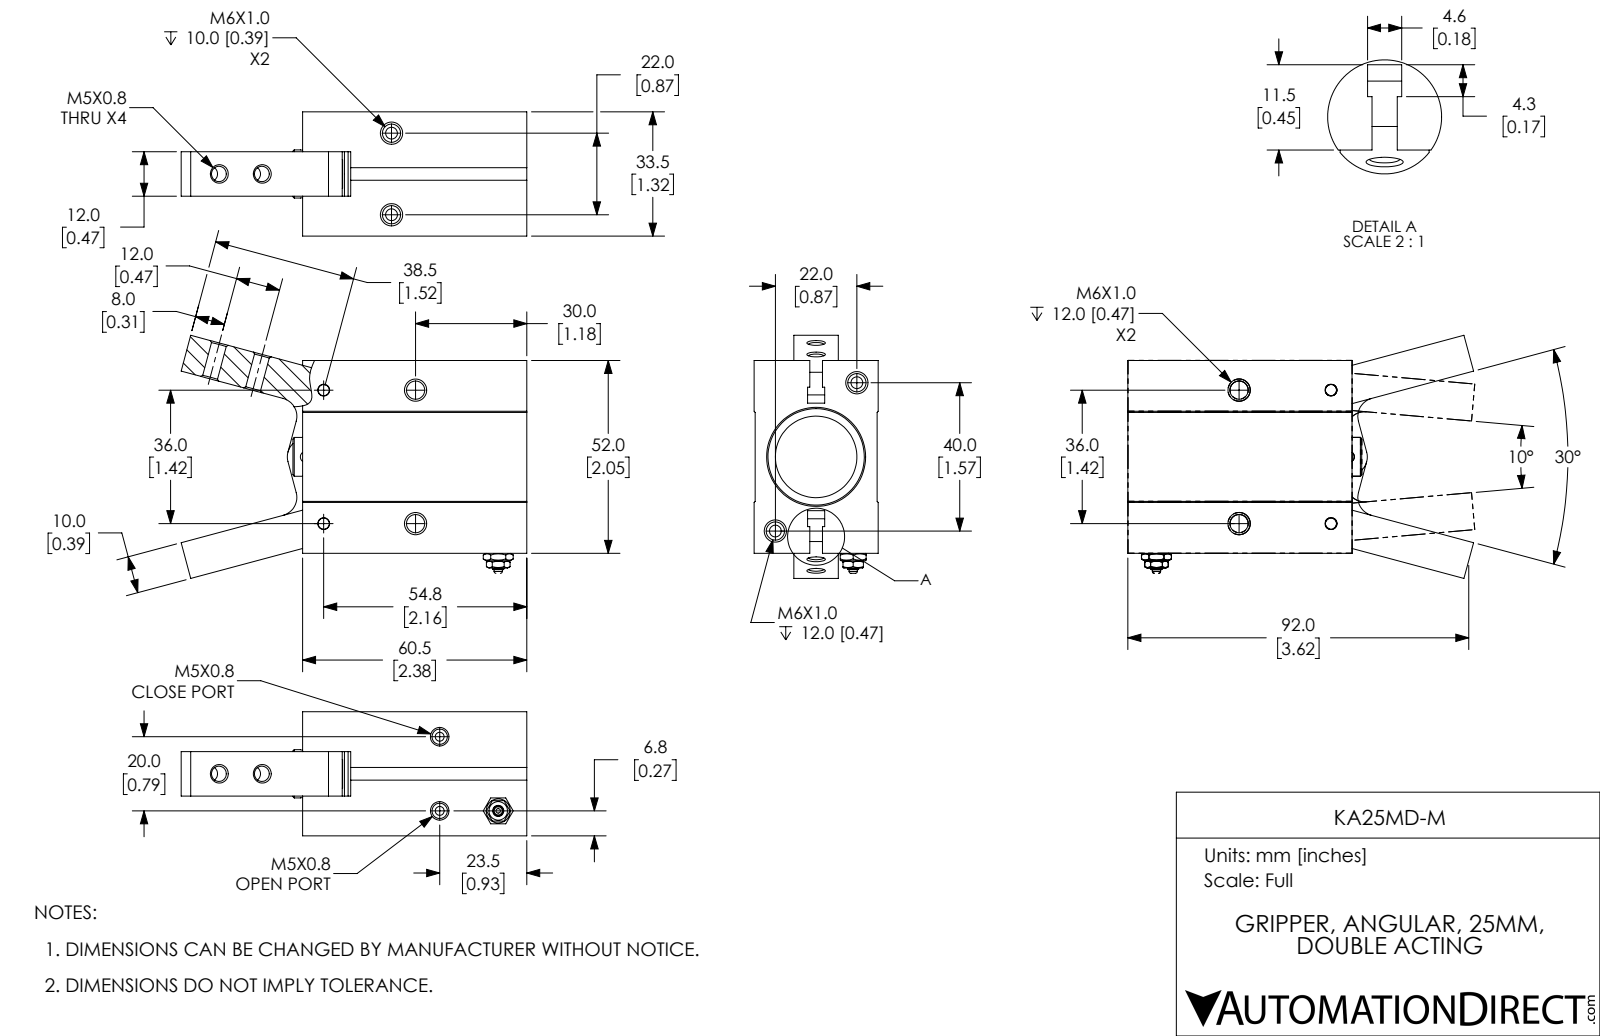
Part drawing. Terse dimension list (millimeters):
name: KA25MD-M-4; KA25MD-M; KA25MD-M-2; KA25MD-M-1 (+1 more)
written by: SolidWorks 2017 (AUTOMOTIVE_DESIGN)
unit: mm
bodies: 4 solids, 273 faces (105 planar, 90 cylindrical, 78 other)
size: 93.28 × 65.59 × 33.5
volume: 91 948 mm³; area: 32 833 mm²
holes: 6× ⌀4.13, 4× ⌀4.92, 3× ⌀3, 2× ⌀4.92, 2× ⌀6.2, 1× ⌀14, 1× ⌀22, 1× ⌀25, 1× ⌀26, 1× ⌀27
bosses: 1× ⌀24.9, 1× ⌀13, 1× ⌀10, 1× ⌀3, 1× ⌀2.2
rounds: 4× R5
face distances: 33.2, 10.75, 22.75, 10.45, 22.45, 32.9, 33.5, 52, 7.7, 4.3
hole spacings: 12, 13.04, 18.63, 22.83, 24.7, 24.8, 34.64, 36
